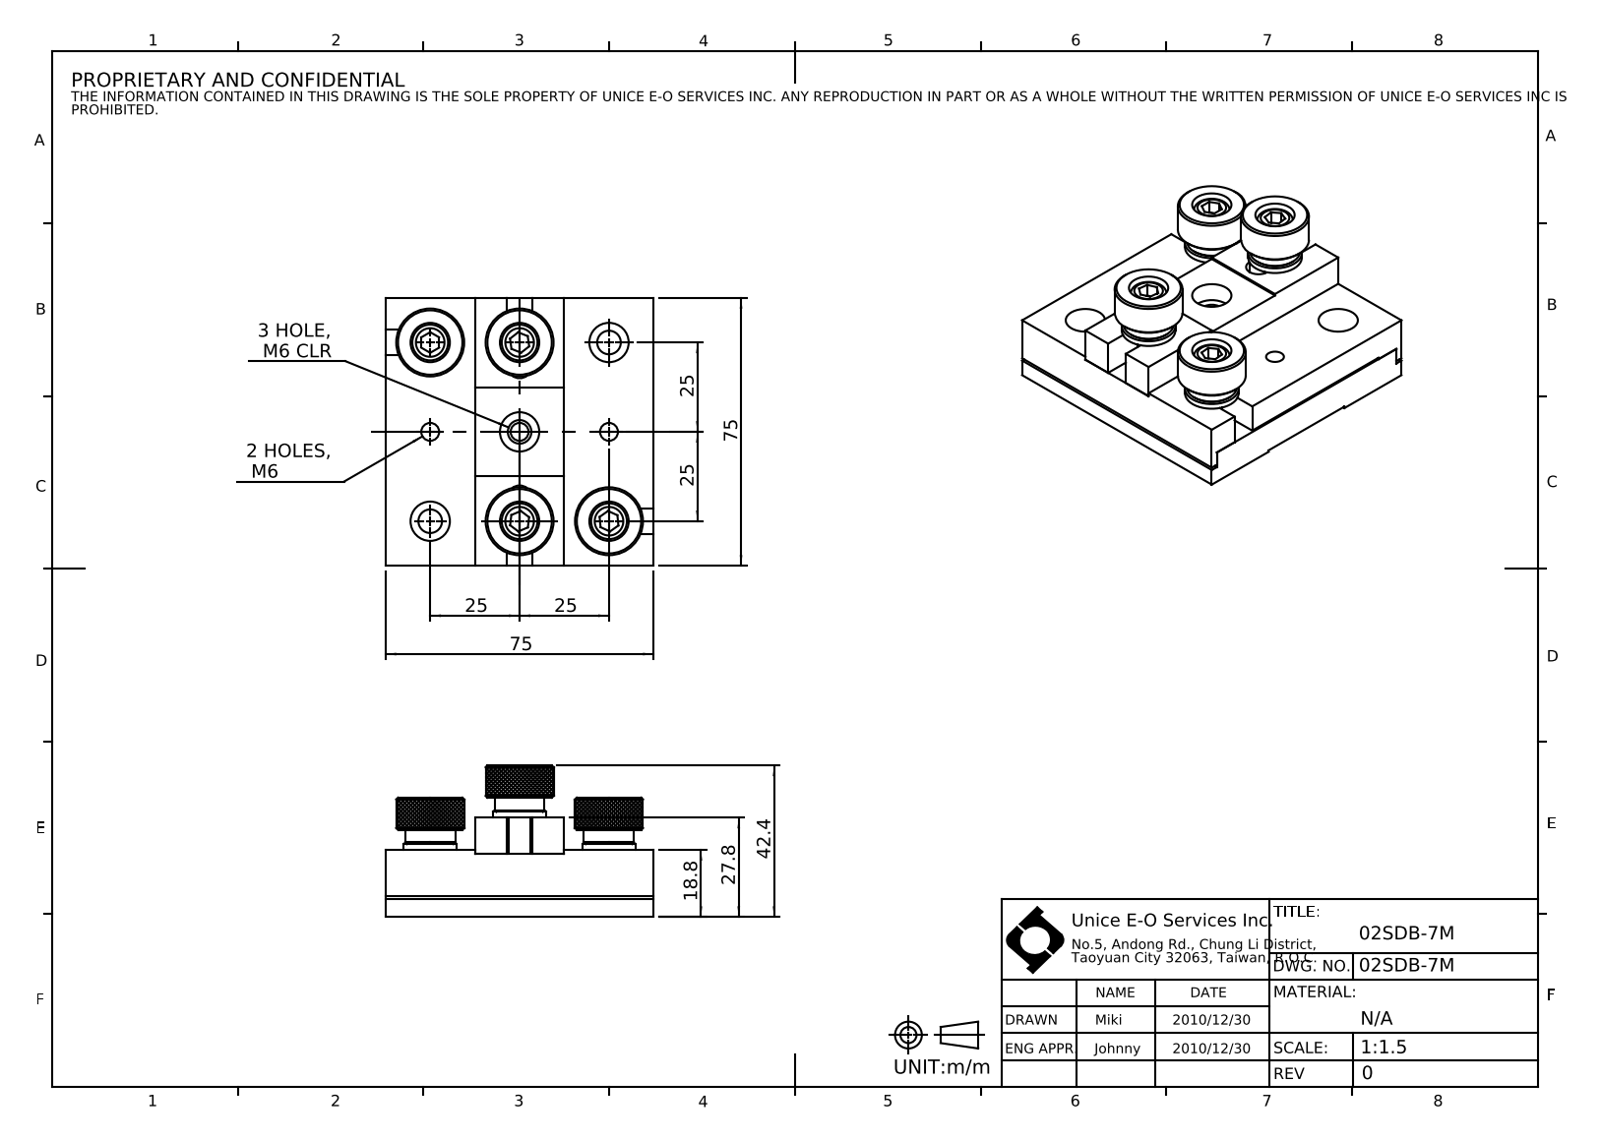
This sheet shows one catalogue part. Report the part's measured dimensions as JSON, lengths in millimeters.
{"part_name": "02SDB-7M", "step_written_by": "SolidWorks 2016 (CONFIG_CONTROL_DESIGN)", "units": "millimeters", "bodies": {"solids": 0, "faces": 204, "planar": 94, "cylindrical": 66, "other": 44}, "overall_size": [75, 75, 42.4], "round_holes": [[11, 7], [5, 4], [6.6, 3]], "round_bosses_or_shafts": [[19, 4], [15, 4], [14, 4], [6, 4]], "partial_cylinders_radius": [[3.5, 2]], "face_to_face_distances": [10, 0.5, 17.3, 8.8, 8.3, 10.5, 18.8, 9, 17.8, 75], "hole_center_spacings": [25, 35.36, 55.9, 50, 70.71]}
